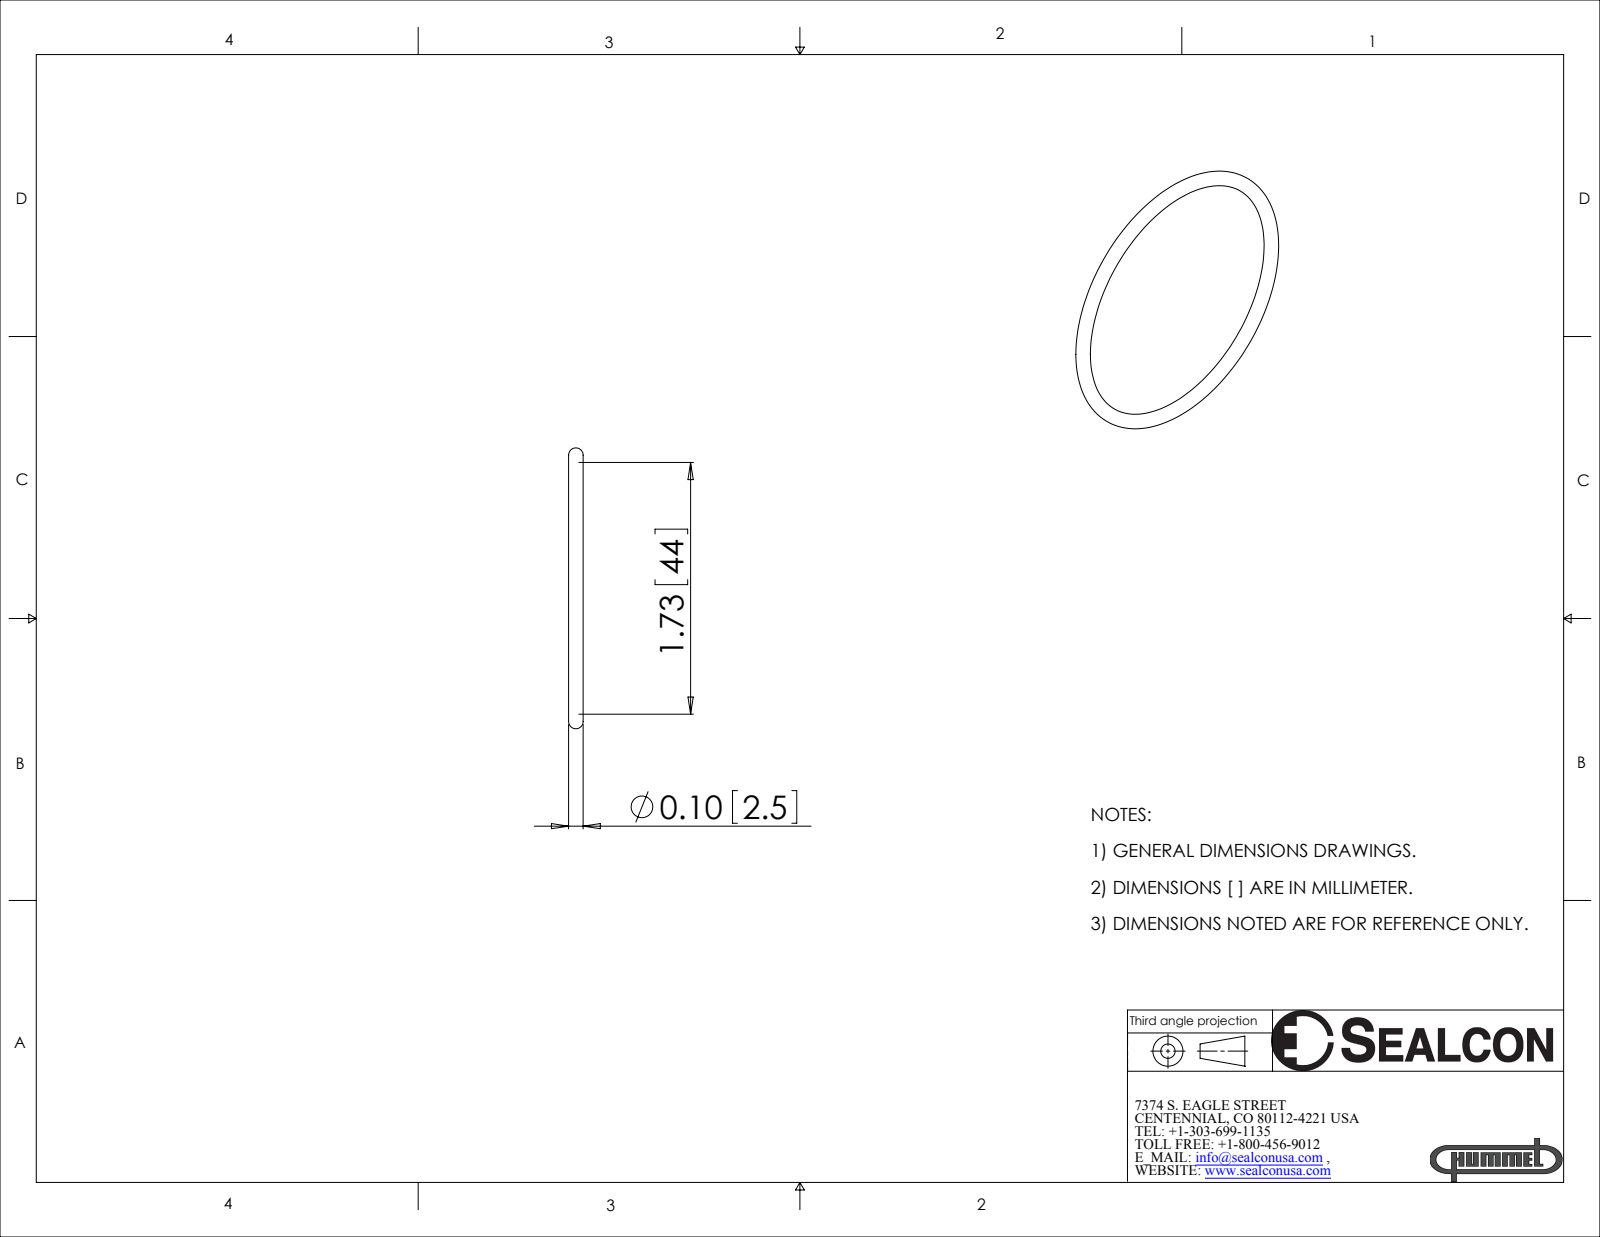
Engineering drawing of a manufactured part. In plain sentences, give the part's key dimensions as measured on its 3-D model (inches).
The part is named "OR-64-SI". Its 3-D file was written by "SolidWorks 2008 (CONFIG_CONTROL_DESIGN)". It is 1 solid with 4 faces: 0 planar, 0 cylindrical and 4 other. Overall it measures 1.93 by 1.93 by 0.1 inches. Its volume is 0.045 cubic inches and its surface area 1.806 square inches.
